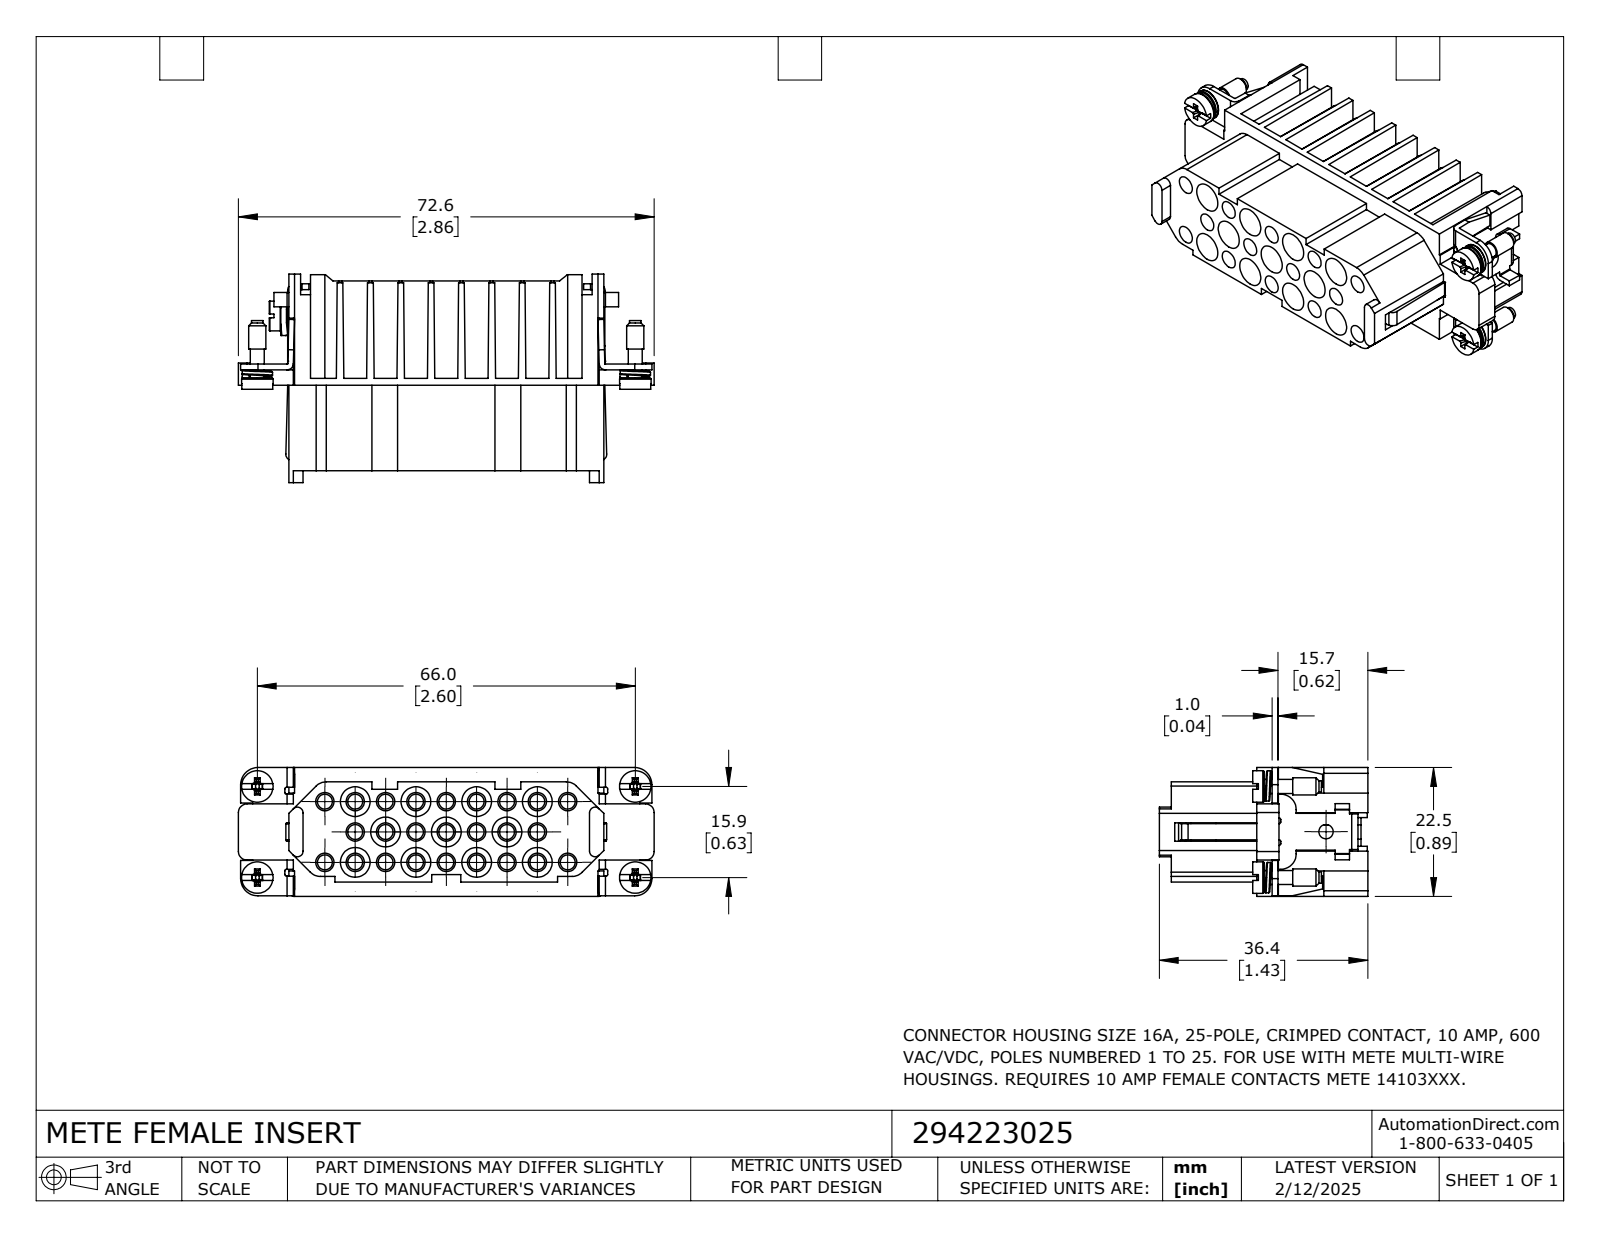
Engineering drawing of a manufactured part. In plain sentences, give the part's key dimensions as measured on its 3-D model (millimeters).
The part is named "294223025". Its 3-D file was written by "SolidWorks 2024 (CONFIG_CONTROL_DESIGN)". It is 13 solids with 1133 faces: 562 planar, 420 cylindrical and 151 other. Overall it measures 72.6 by 36.4 by 22.5 millimeters. Its volume is 21 170 cubic millimeters and its surface area 24 540 square millimeters. Round holes: 25 of diameter 2.6, 25 of diameter 3.2, 25 of diameter 3.5, 25 of diameter 4.1, 11 of diameter 5.2, 5 of diameter 2.5, 4 of diameter 2.9, 1 of diameter 3. Round bosses or shafts: 4 of diameter 5.5, 4 of diameter 5.3, 4 of diameter 3, 4 of diameter 2.4, 4 of diameter 2, 1 of diameter 5.2, 1 of diameter 2.9. Partial cylindrical surfaces (rounded edges, fillets, slot ends): 32 of radius 0.3, 18 of radius 2.8, 12 of radius 0.1, 12 of radius 0.3, 12 of radius 1.1, 8 of radius 1, 4 of radius 1.5, 4 of radius 2.5. The main face-to-face distances are 10.6, 5.3, 15.9, 21.2, 1, 2.5, 1.2, 26.5, 20, 14.9. The hole center spacings are 11.9, 5.3, 7.5, 10.6, 16.8, 15.9, 21.8, 15.
